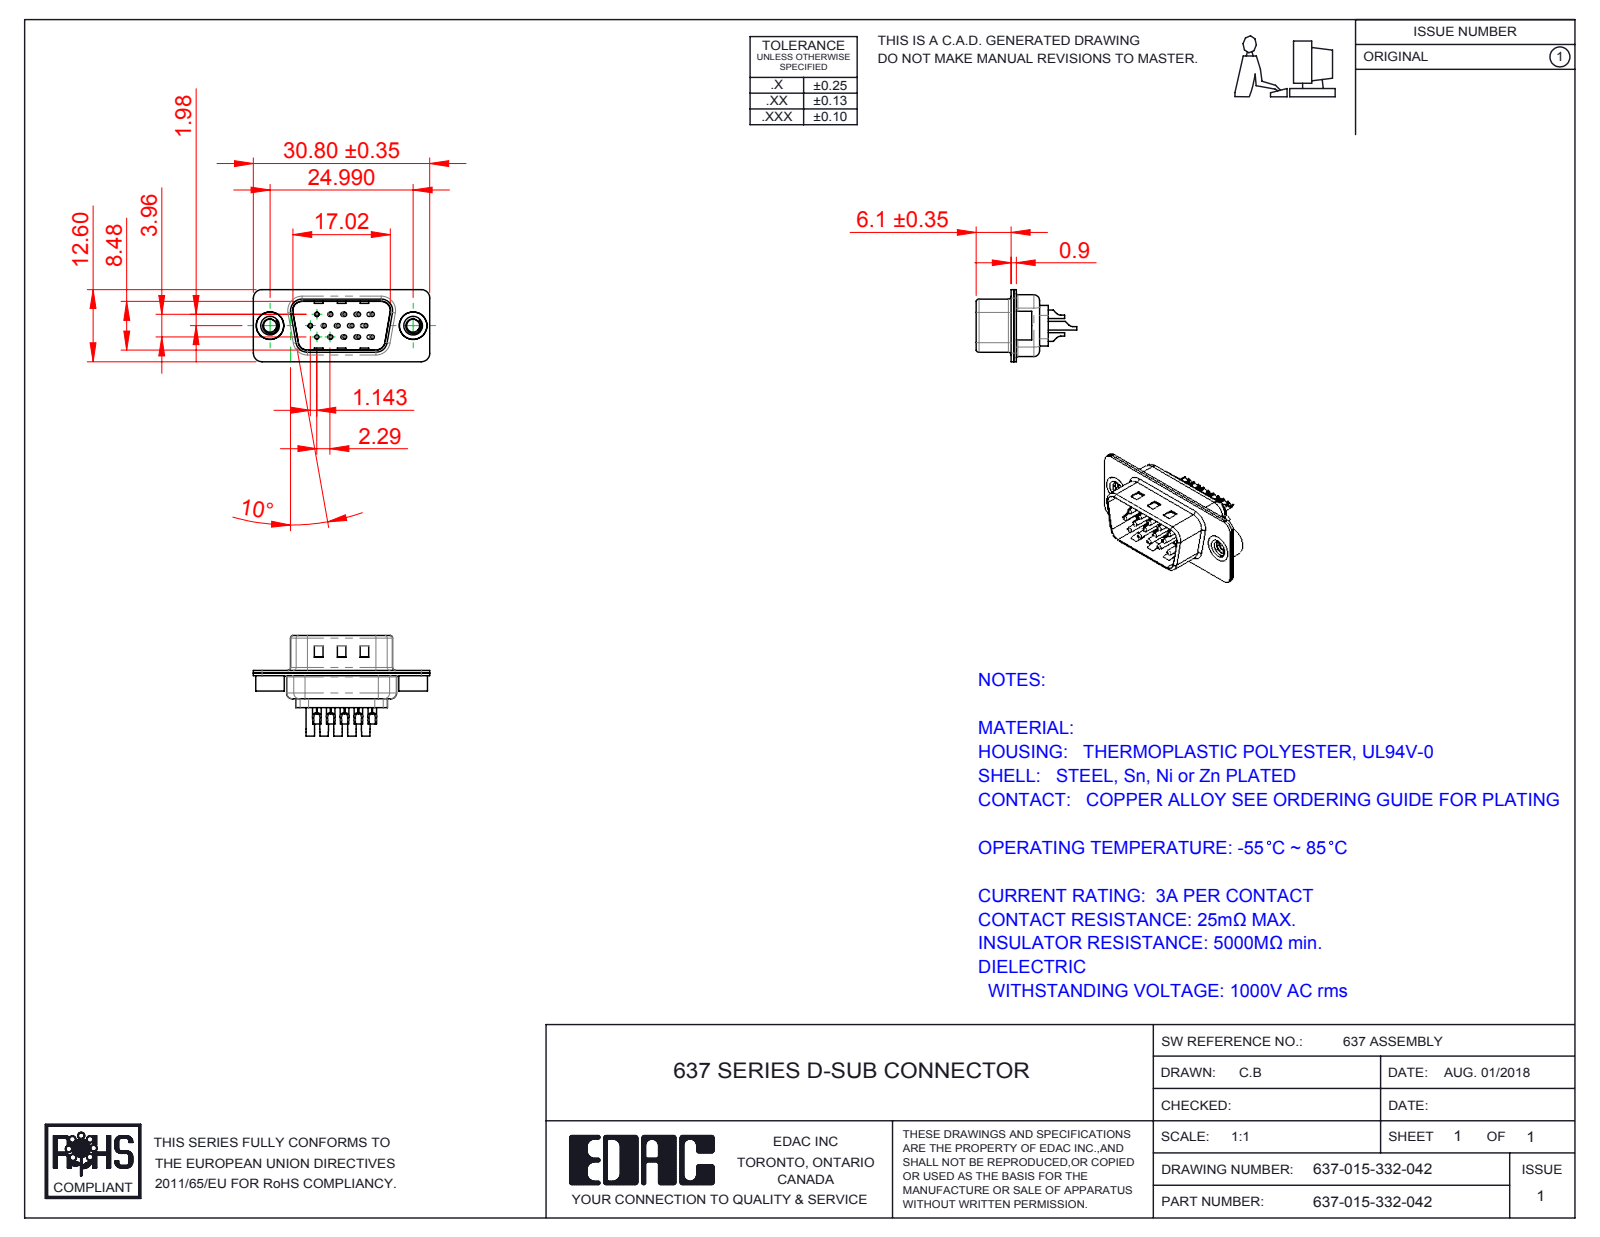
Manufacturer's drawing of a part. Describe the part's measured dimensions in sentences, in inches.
The part is named "637 Contact Row 3_32; 637 Housing_15 Contacts; 637 Contact Row 2_32; 637 Contact Row 1_32 (+4 more)". Its 3-D file was written by "SolidWorks 2016 (CONFIG_CONTROL_DESIGN)". It is 20 solids with 1264 faces: 317 planar, 564 cylindrical and 383 other. Overall it measures 1.213 by 0.691 by 0.496 inches. Its volume is 0.081 cubic inches and its surface area 7.407 square inches. Round holes: 27 of diameter 0.063, 15 of diameter 0.014, 15 of diameter 0.043, 12 of diameter 0.03, 12 of diameter 0.079, 2 of diameter 0.089, 2 of diameter 0.157, 2 of diameter 0.189. Round bosses or shafts: 15 of diameter 0.079, 15 of diameter 0.059, 15 of diameter 0.03, 2 of diameter 0.197, 2 of diameter 0.193. Partial cylindrical surfaces (rounded edges, fillets, slot ends): 16 of radius 0.059, 12 of radius 0.079, 8 of radius 0.02, 7 of radius 0.039, 4 of radius 0.01, 4 of radius 0.022, 4 of radius 0.028, 4 of radius 0.037. The main face-to-face distances are 0.018, 0.035, 0.016, 0.028, 0.334, 0.35, 0.012, 0.179, 0.041, 0.046. The hole center spacings are 0.156, 0.09, 0.09, 0.18, 0.095, 0.238, 0.191, 0.093.
